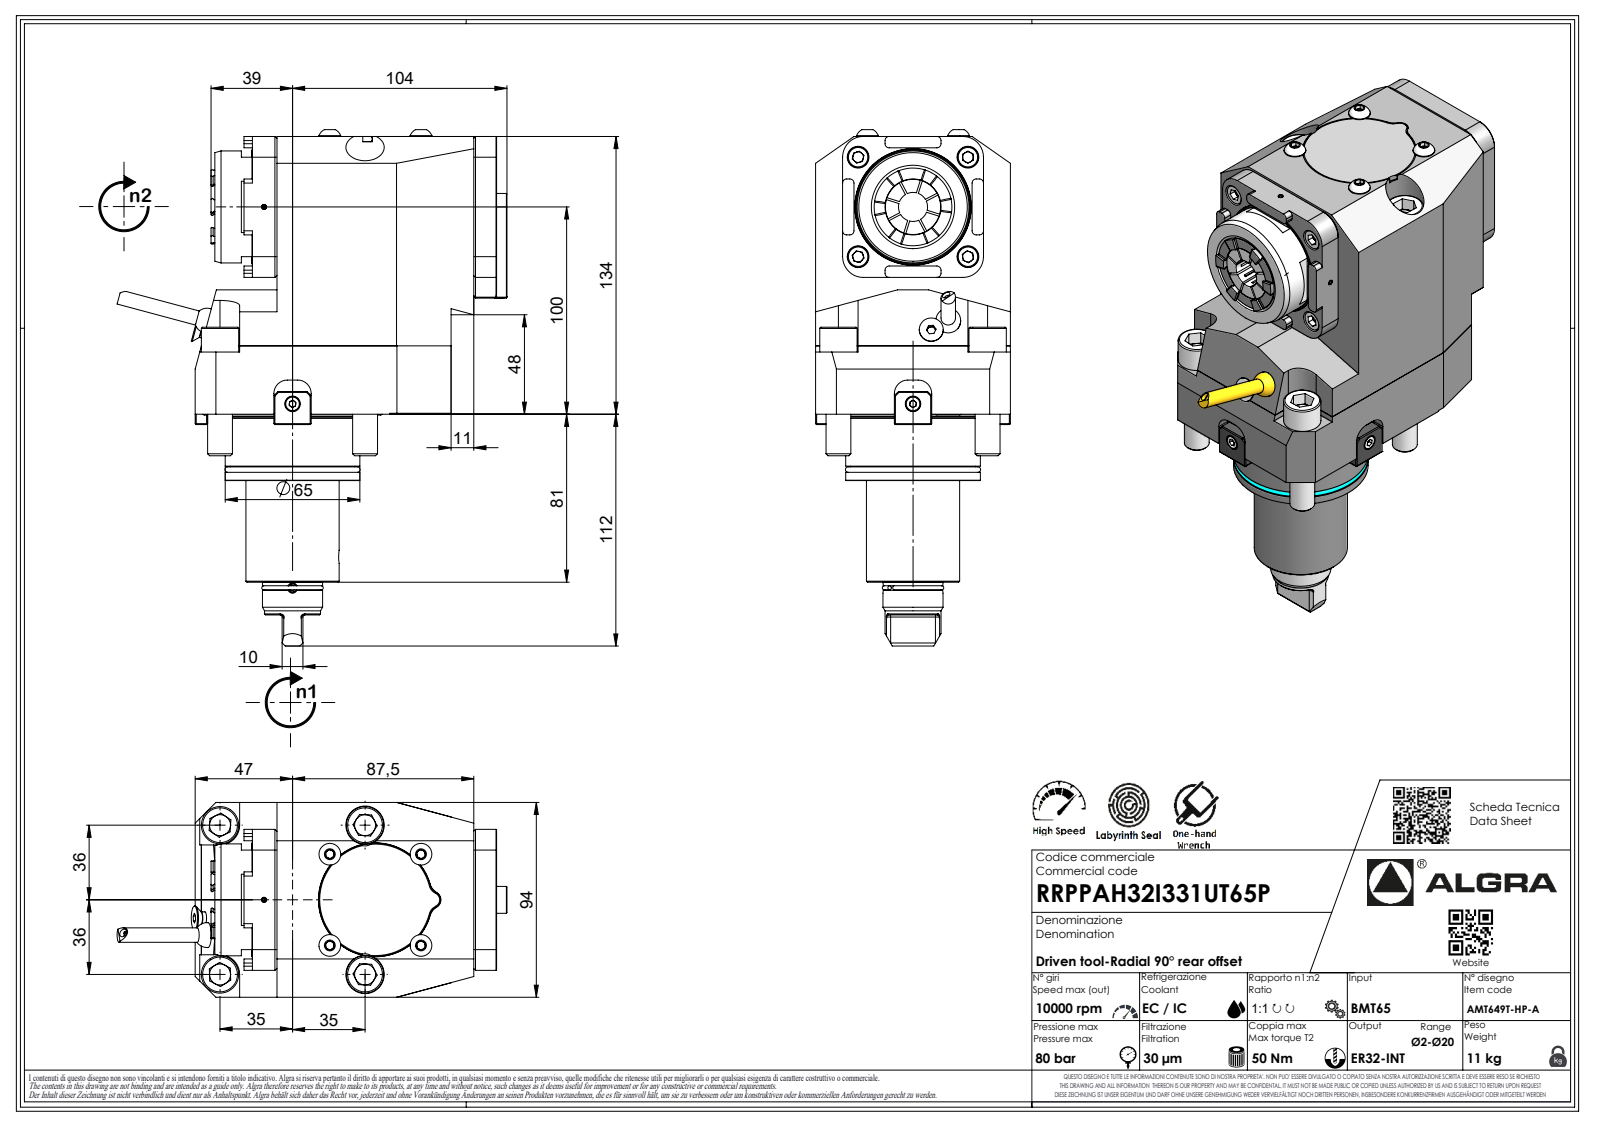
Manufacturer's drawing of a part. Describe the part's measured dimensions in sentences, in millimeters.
The part is named "RRPPAH32I331UT65P". Its 3-D file was written by "SolidWorks 2023 (AUTOMOTIVE_DESIGN)". It is 1 solid with 625 faces: 395 planar, 84 cylindrical and 146 other. Overall it measures 249.1 by 188.16 by 94 millimeters. Its volume is 1 628 000 cubic millimeters and its surface area 106 954 square millimeters. Round holes: 1 of diameter 2.1. Round bosses or shafts: 4 of diameter 12, 4 of diameter 10.5, 2 of diameter 18, 1 of diameter 65, 1 of diameter 64.6, 1 of diameter 60.2, 1 of diameter 54, 1 of diameter 45. Partial cylindrical surfaces (rounded edges, fillets, slot ends): 16 of radius 2, 7 of radius 0.33, 7 of radius 0.52, 7 of radius 3.7, 6 of radius 1, 6 of radius 10, 2 of radius 9.5, 1 of radius 0.21. The main face-to-face distances are 94, 134, 22, 11, 81, 133.5, 0.5, 84, 106, 30.
